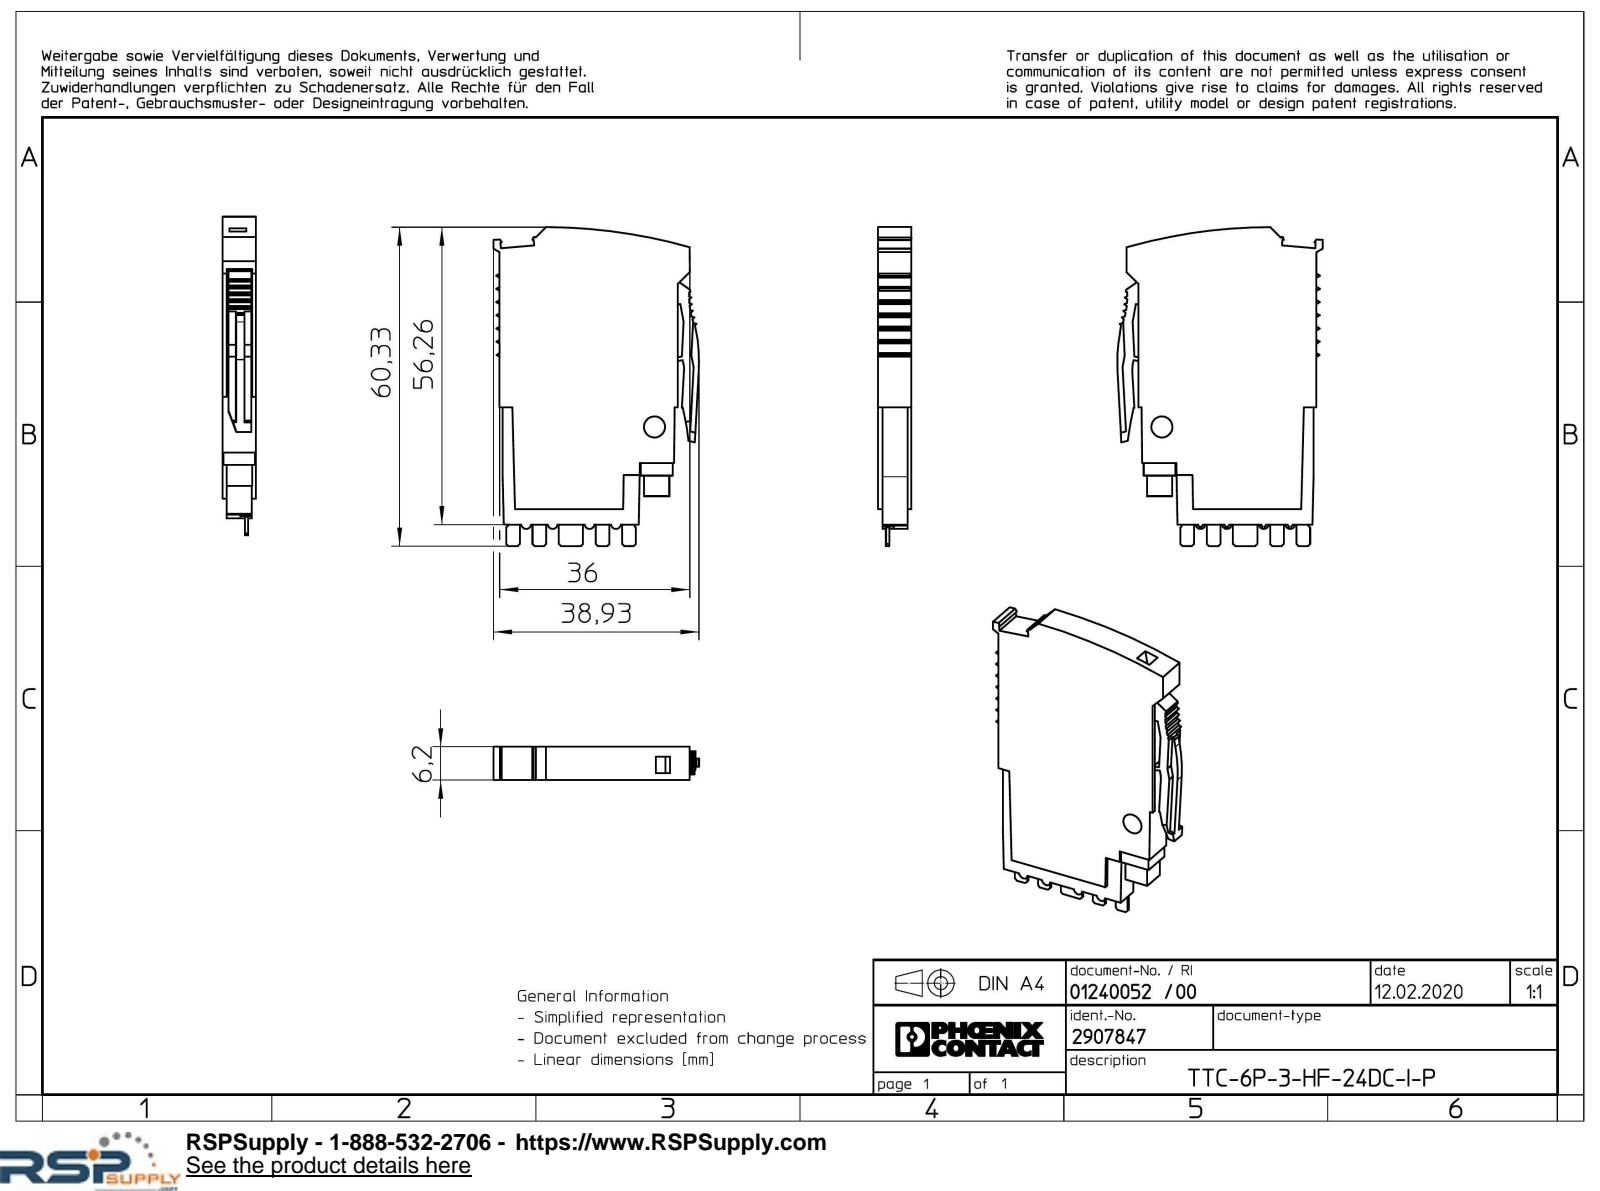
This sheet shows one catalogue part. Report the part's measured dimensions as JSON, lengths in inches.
{"part_name": "TTC-M_P-select", "step_written_by": "Creo Elements/Direct Modeling 20.1A 29-Sep-2018 (C) Parametric Technology GmbH (AUTOMOTIVE_DESIGN)", "units": "inches", "bodies": {"solids": 1, "faces": 223, "planar": 189, "cylindrical": 34, "other": 0}, "overall_size": [2.375, 1.533, 0.248], "volume_in3": 0.68, "surface_area_in2": 8.694, "round_holes": [[0.157, 1]], "partial_cylinders_radius": [[0.02, 4], [0.037, 4], [0.079, 1], [0.197, 1], [0.591, 1], [1.181, 1], [1.969, 1], [3.937, 1]], "face_to_face_distances": [0.248, 0.032, 0.219, 0.029, 0.187, 0.216, 0.021, 0.024, 0.024, 0.048]}
